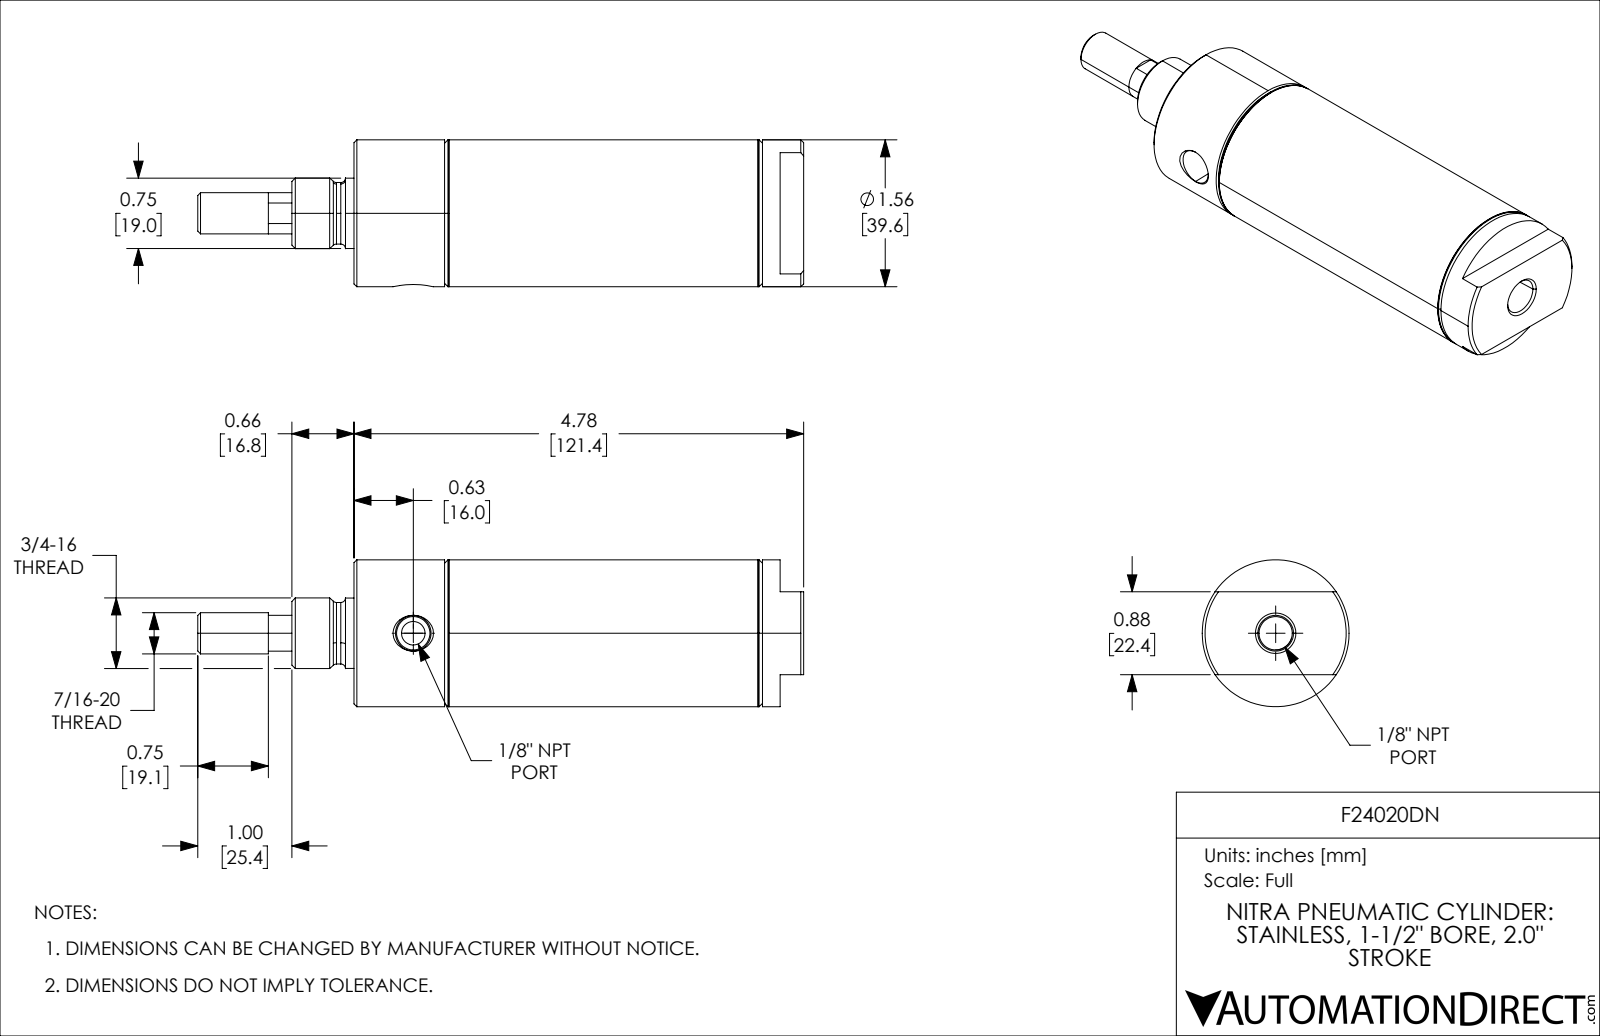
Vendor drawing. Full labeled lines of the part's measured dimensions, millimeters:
Part name (STEP PRODUCT): F24020DN_3; F24020DN_7; F24020DN_9; F24020DN (+1 more)
STEP written by: SolidWorks 2021 (CONFIG_CONTROL_DESIGN)
Units: millimetres
Bodies: 4 solids, 126 faces (28 planar, 42 cylindrical, 56 other)
Overall size (bounding box): 163.53 × 39.62 × 39.62
Volume: 94 760 mm³ · Surface area: 45 716 mm²
Round holes (diameter × count): ⌀6.35 ×1, ⌀11.73 ×1, ⌀24.71 ×1, ⌀36.36 ×1
Round bosses / shafts (diameter × count): ⌀39.62 ×1, ⌀38.39 ×1, ⌀19.05 ×1, ⌀18.99 ×1, ⌀16.6 ×1, ⌀11.13 ×1, ⌀11.11 ×1
Main face-to-face distances: 22.22, 6.35, 11.13, 50.8, 73.02, 30.86, 81.66, 103.88, 121.36, 90.5
